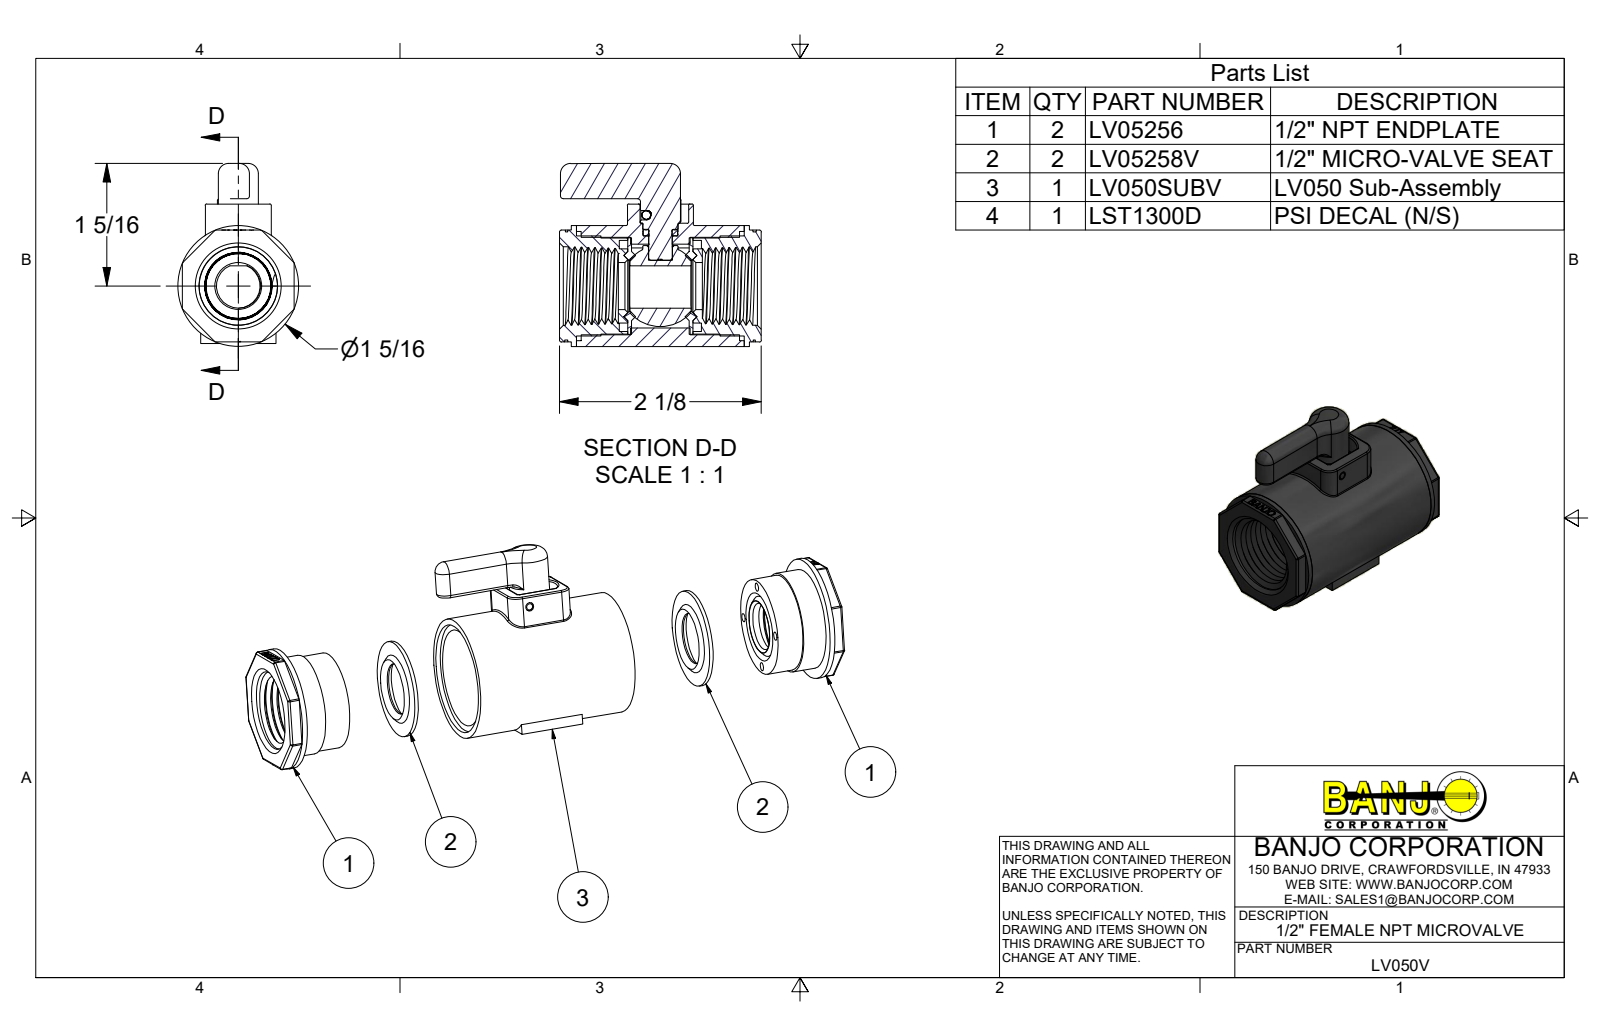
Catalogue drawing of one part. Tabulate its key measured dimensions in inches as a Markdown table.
| quantity | value |
| --- | --- |
| part name | LV050V; LV050SUBV; LV05254A; LV02153B (+5 more) |
| STEP written by | Autodesk Inventor 2012 (AUTOMOTIVE_DESIGN) |
| units | inches |
| bodies | 9 solids, 664 faces (280 planar, 139 cylindrical, 245 other) |
| overall size | 2.142 × 1.944 × 1.285 |
| volume | 2.145 in³ |
| surface area | 39.54 in² |
| round holes (diameter × count) | 0.09 × 4, 0.093 × 1, 0.251 × 1, 0.368 × 1, 0.376 × 1, 0.47 × 1, 0.5 × 1, 0.541 × 1, 0.89 × 1, 1.034 × 1, 1.16 × 1 |
| round bosses / shafts (diameter × count) | 1.285 × 1, 1.062 × 1, 1.024 × 1, 1.02 × 1, 0.425 × 1, 0.375 × 1, 0.372 × 1, 0.25 × 1 |
| partial cylindrical surfaces (radius × count) | 0.02 × 24, 0.01 × 16, 0.015 × 14, 0.125 × 4, 0.03 × 2, 0.05 × 2, 0.109 × 2, 0.25 × 2 |
| main face-to-face distances | 0.545, 1.237, 0.18, 0.725, 1.417, 1.962, 0.04, 0.765, 1.377, 0.585 |
| hole center spacings | 0.439, 0.62, 0.877 |
